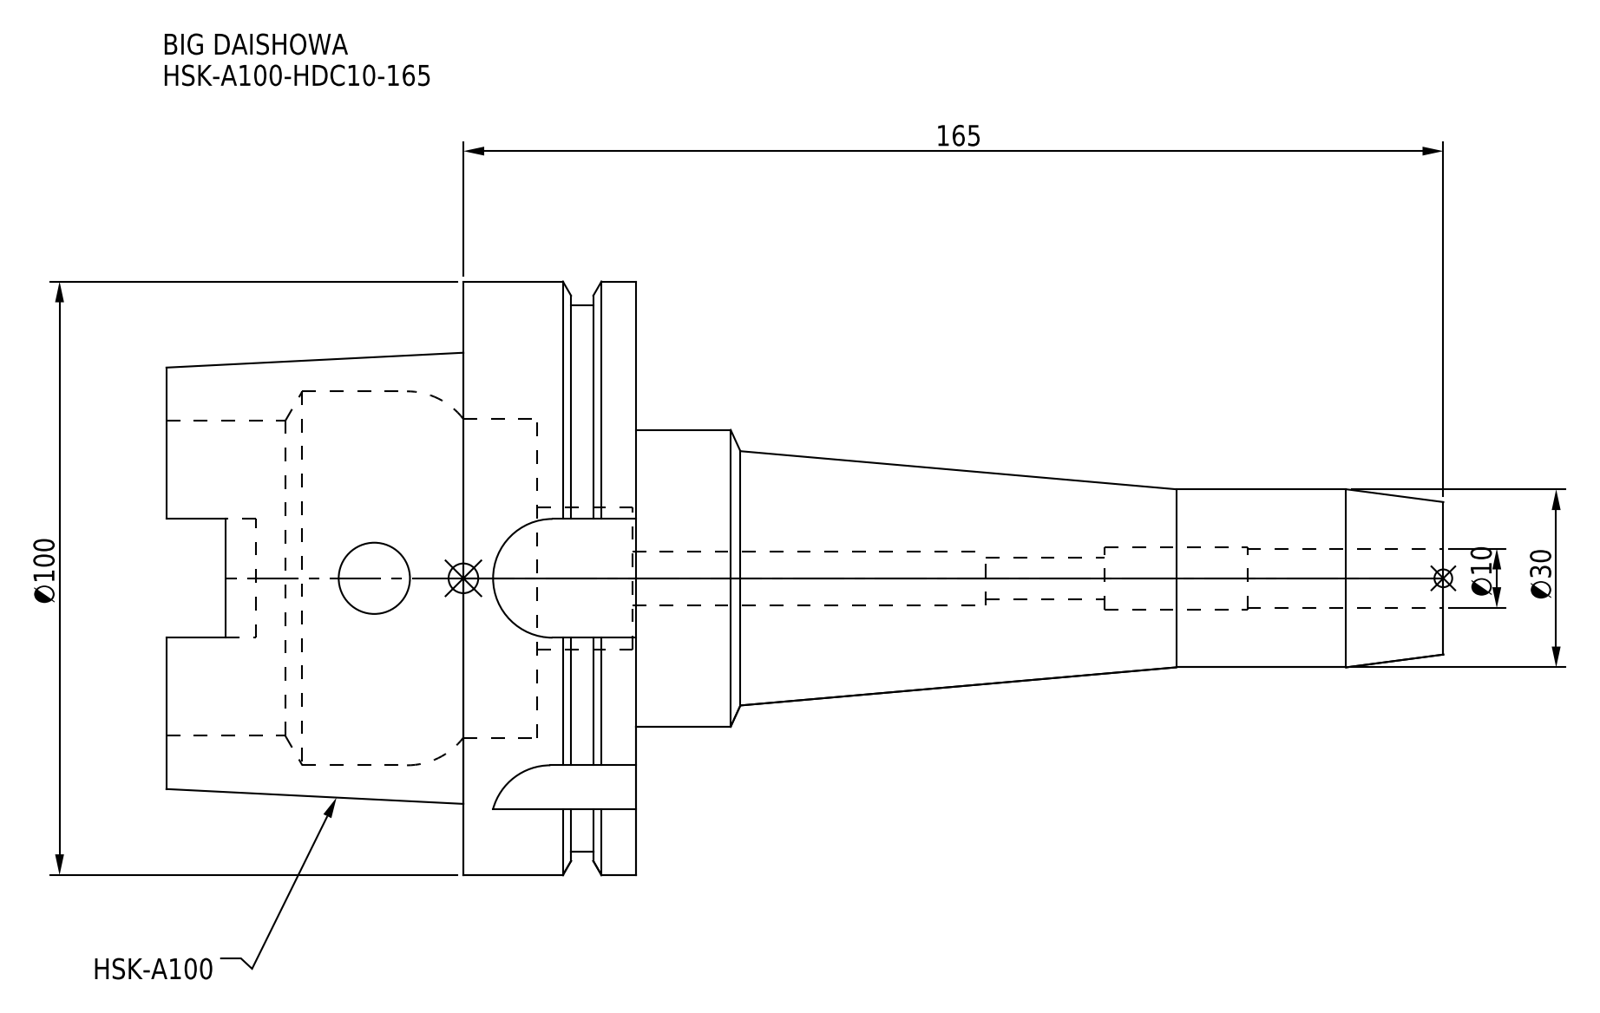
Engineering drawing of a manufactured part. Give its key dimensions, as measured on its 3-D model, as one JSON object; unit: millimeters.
{"part_name": "HSK-A100-HDC10-165", "step_written_by": "CREO PARAMETRIC BY PTC INC, 2016380 (AUTOMOTIVE_DESIGN)", "units": "millimeters", "bodies": {"solids": 1, "faces": 97, "planar": 35, "cylindrical": 42, "other": 20}, "overall_size": [215, 100, 100], "volume_mm3": 385902, "surface_area_mm2": 68096, "round_holes": [[7, 1], [9, 1], [10, 1], [10.5, 1], [12, 1], [24, 1], [53, 1], [53.8, 1], [63, 1]], "round_bosses_or_shafts": [[100, 1], [92, 1], [50, 1], [30, 1]], "partial_cylinders_radius": [[4.88, 4], [10, 4]], "face_to_face_distances": [29, 16.55, 12.45, 79, 62.45, 50, 88, 136, 152.55, 165]}
